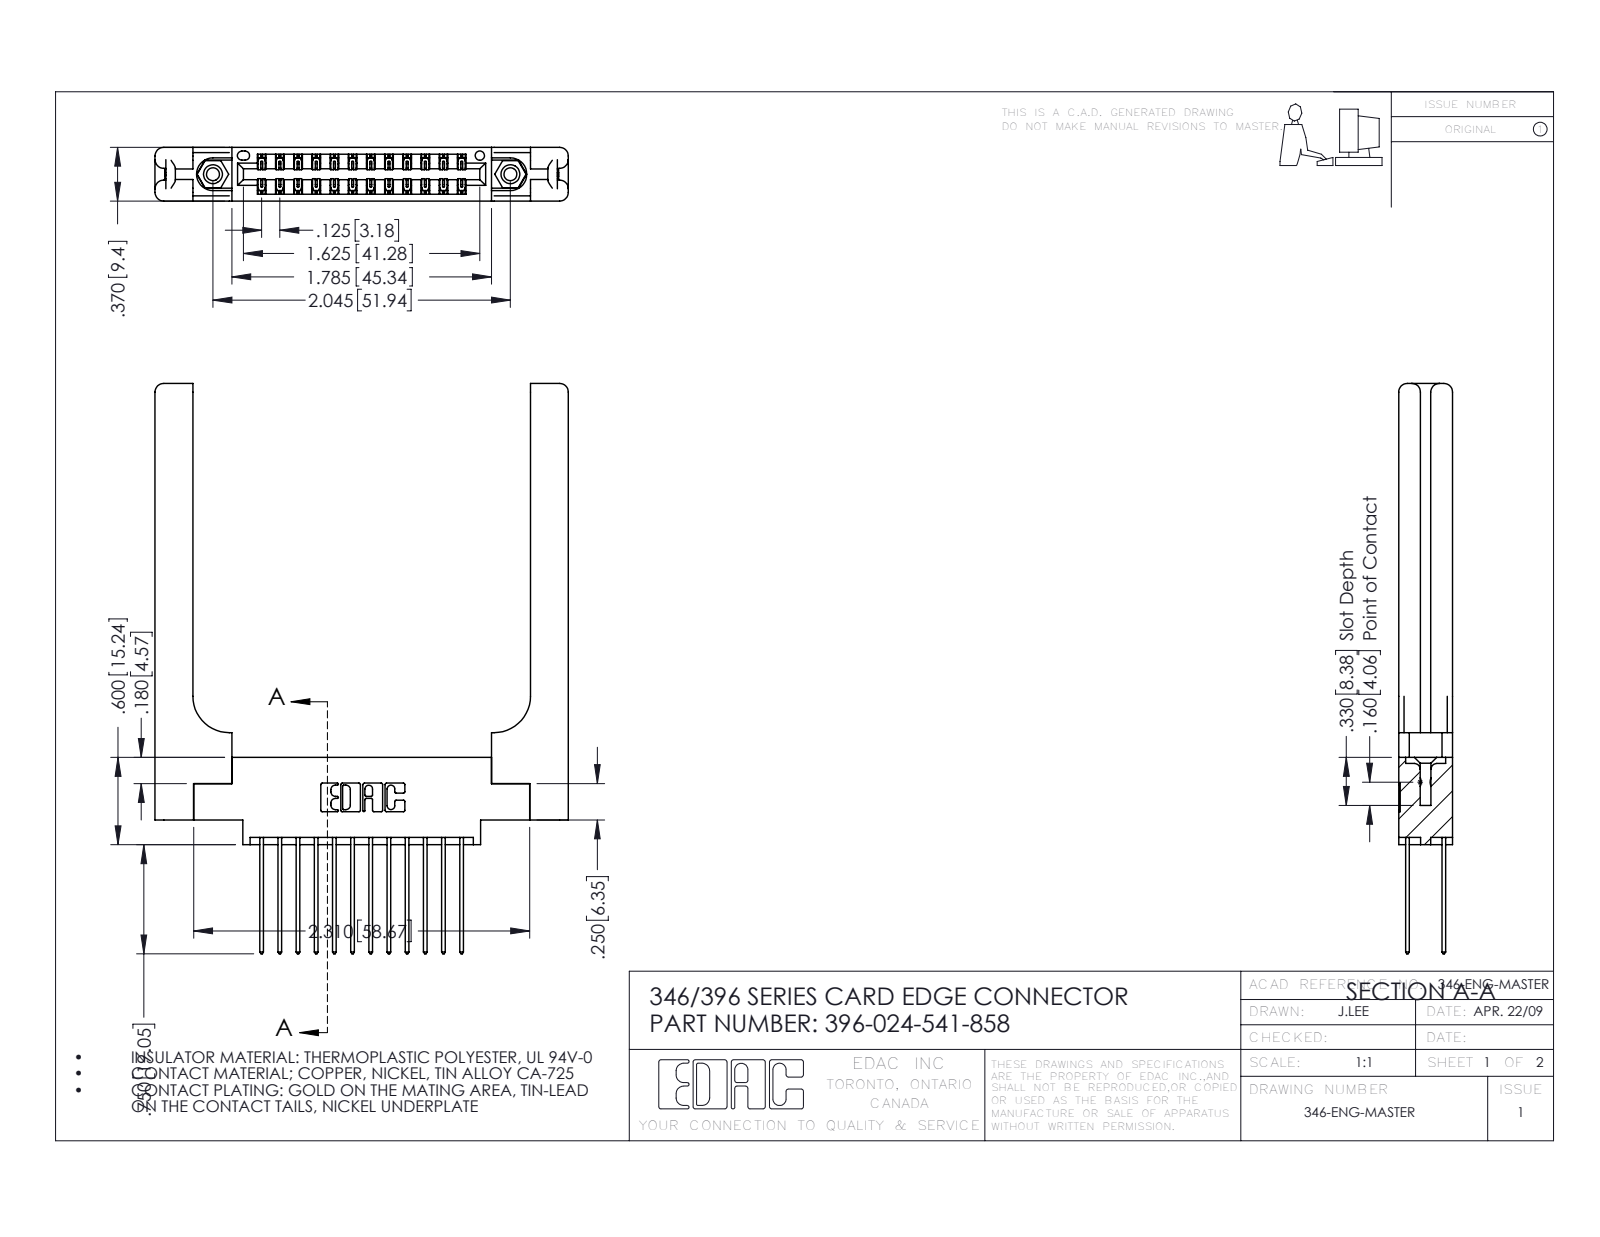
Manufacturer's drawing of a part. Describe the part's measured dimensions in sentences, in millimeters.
The part is named "346 Part_0.170 Offset - 0.156 Dia-TH; 396-024-541-858; 346-220-058_345-220-058; 345-250-001_345-250-001-102 (+1 more)". Its 3-D file was written by "SolidWorks 2016 (CONFIG_CONTROL_DESIGN)". It is 29 solids with 1630 faces: 1068 planar, 502 cylindrical and 60 other. Overall it measures 99.6 by 72.2 by 9.4 millimeters. Its volume is 14 300 cubic millimeters and its surface area 14 670 square millimeters. Round holes: 2 of diameter 2.3, 2 of diameter 3.2, 2 of diameter 4, 1 of diameter 1.6. Round bosses or shafts: 2 of diameter 3.9. Partial cylindrical surfaces (rounded edges, fillets, slot ends): 36 of radius 0.2, 24 of radius 0.3, 22 of radius 0.3, 16 of radius 1.5, 6 of radius 0.2, 6 of radius 0.8, 3 of radius 0.7, 2 of radius 0.4. The main face-to-face distances are 9.4, 1.8, 3.8, 3.8, 1.2, 8.2, 6.4, 0.6, 2, 7.6. The hole center spacings are 6.2, 46.7, 51.9.
